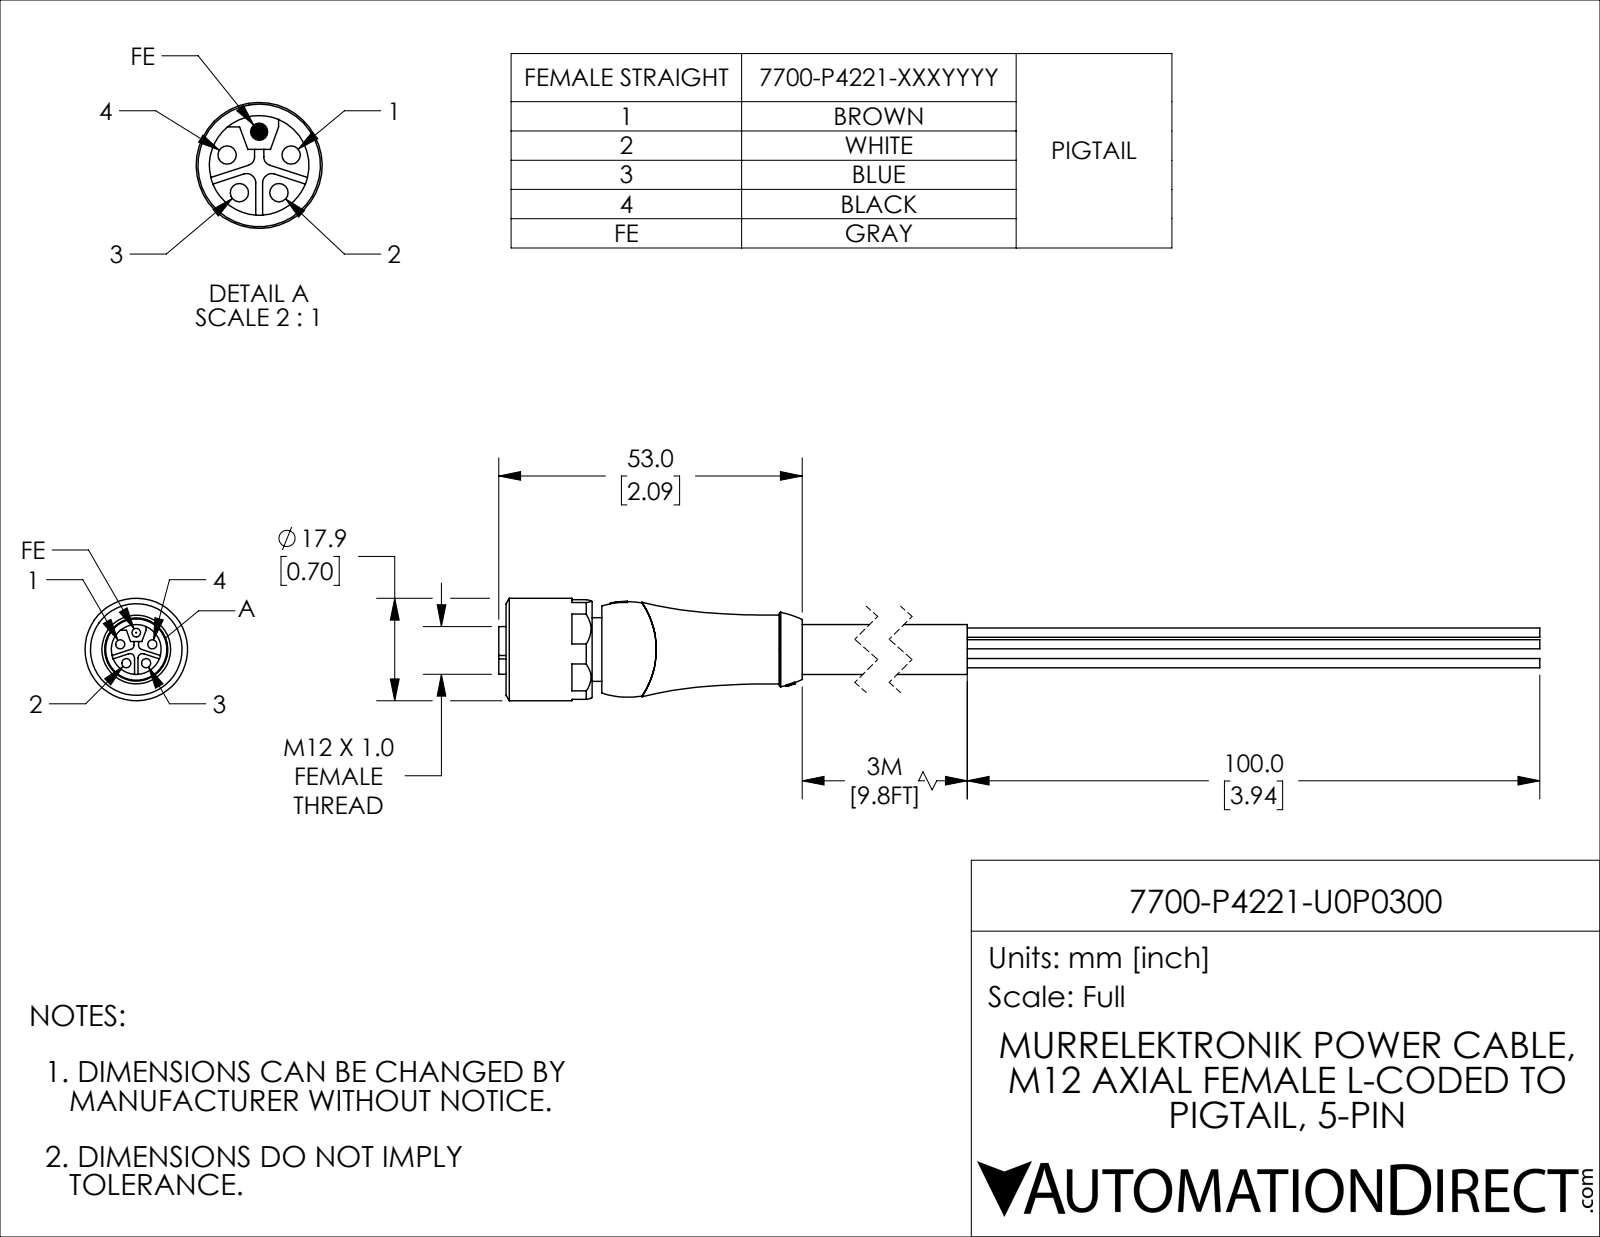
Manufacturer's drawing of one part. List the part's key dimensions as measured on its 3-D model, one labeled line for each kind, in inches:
Part name (STEP PRODUCT): 7700-P4221-U0P0300
STEP written by: SolidWorks 2021 (CONFIG_CONTROL_DESIGN)
Units: inches
Bodies: 2 solids, 142 faces (69 planar, 40 cylindrical, 33 other)
Overall size (bounding box): 7.598 × 0.705 × 0.705
Volume: 0.735 in³ · Surface area: 12.83 in²
Round holes (diameter × count): ⌀0.063 ×4, ⌀0.433 ×1, ⌀0.512 ×1
Round bosses / shafts (diameter × count): ⌀0.705 ×1, ⌀0.51 ×1, ⌀0.437 ×1, ⌀0.343 ×1, ⌀0.063 ×1, ⌀0.059 ×1
Partial cylindrical surfaces — rounded edges, fillets, slot ends (radius × count): R0.031 ×4
Main face-to-face distances: 0.657, 0.591, 0.067, 0.667, 3.61, 3.02, 2.953, 0.181, 0.362, 0.228
Hole centre spacings: 0.116, 0.136, 0.22
